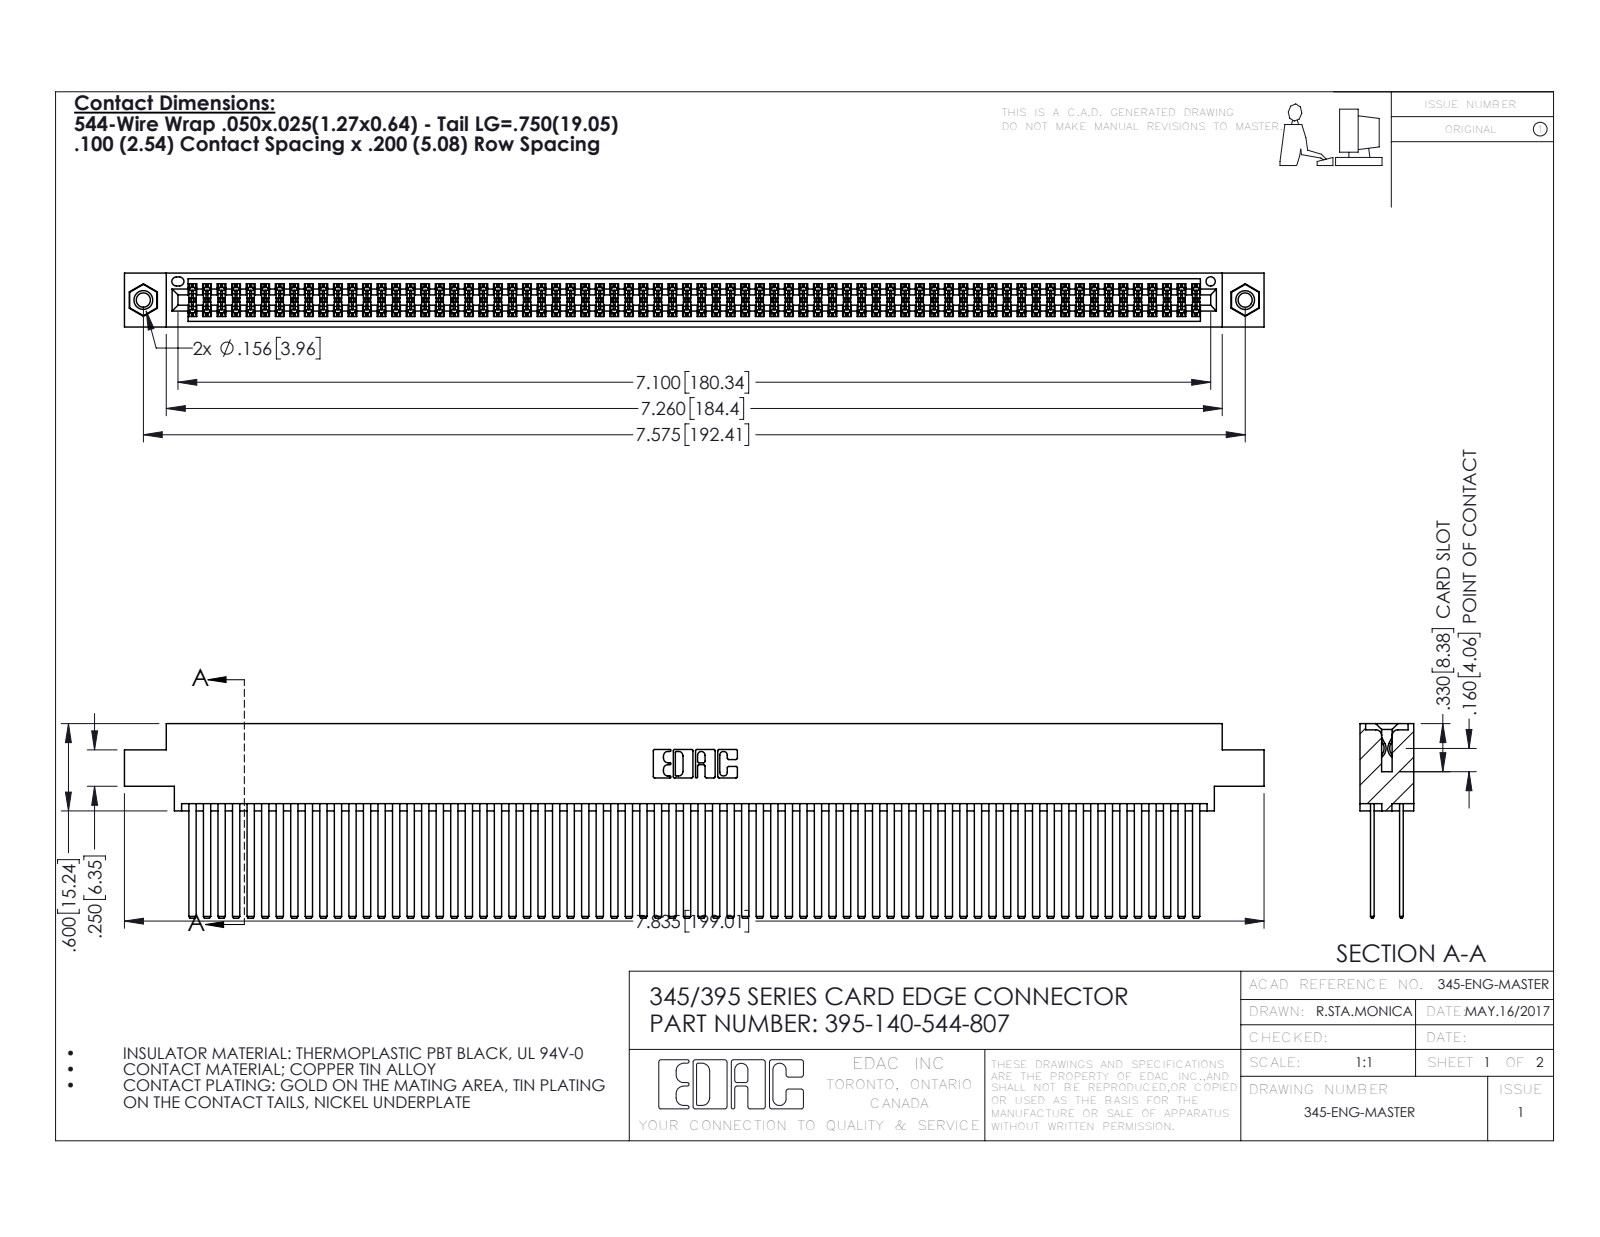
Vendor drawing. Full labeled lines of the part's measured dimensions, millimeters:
Part name (STEP PRODUCT): 395-140-544-807; 345 Part_0.170 Offset - 0.156 Dia-TI; 345-292-001_345-293-144; 345-250-001_345-250-005-103
STEP written by: SolidWorks 2016 (CONFIG_CONTROL_DESIGN)
Units: millimetres
Bodies: 143 solids, 6350 faces (4176 planar, 2158 cylindrical, 16 other)
Overall size (bounding box): 199 × 34 × 9.4
Volume: 21 430 mm³ · Surface area: 38 140 mm²
Round holes (diameter × count): ⌀2.5 ×2, ⌀3.2 ×2, ⌀4 ×2, ⌀1.6 ×1
Round bosses / shafts (diameter × count): ⌀3.9 ×2
Partial cylindrical surfaces — rounded edges, fillets, slot ends (radius × count): R0.2 ×210, R0.3 ×22, R0.2 ×6, R0.8 ×6, R0.7 ×3, R0.4 ×2, R0.5 ×2, R0.6 ×2
Main face-to-face distances: 5.1, 0.6, 1.8, 2.5, 6.9, 7.6, 5.7, 4.4, 9.4, 3.8
Hole centre spacings: 6.9, 186.4, 192.4
